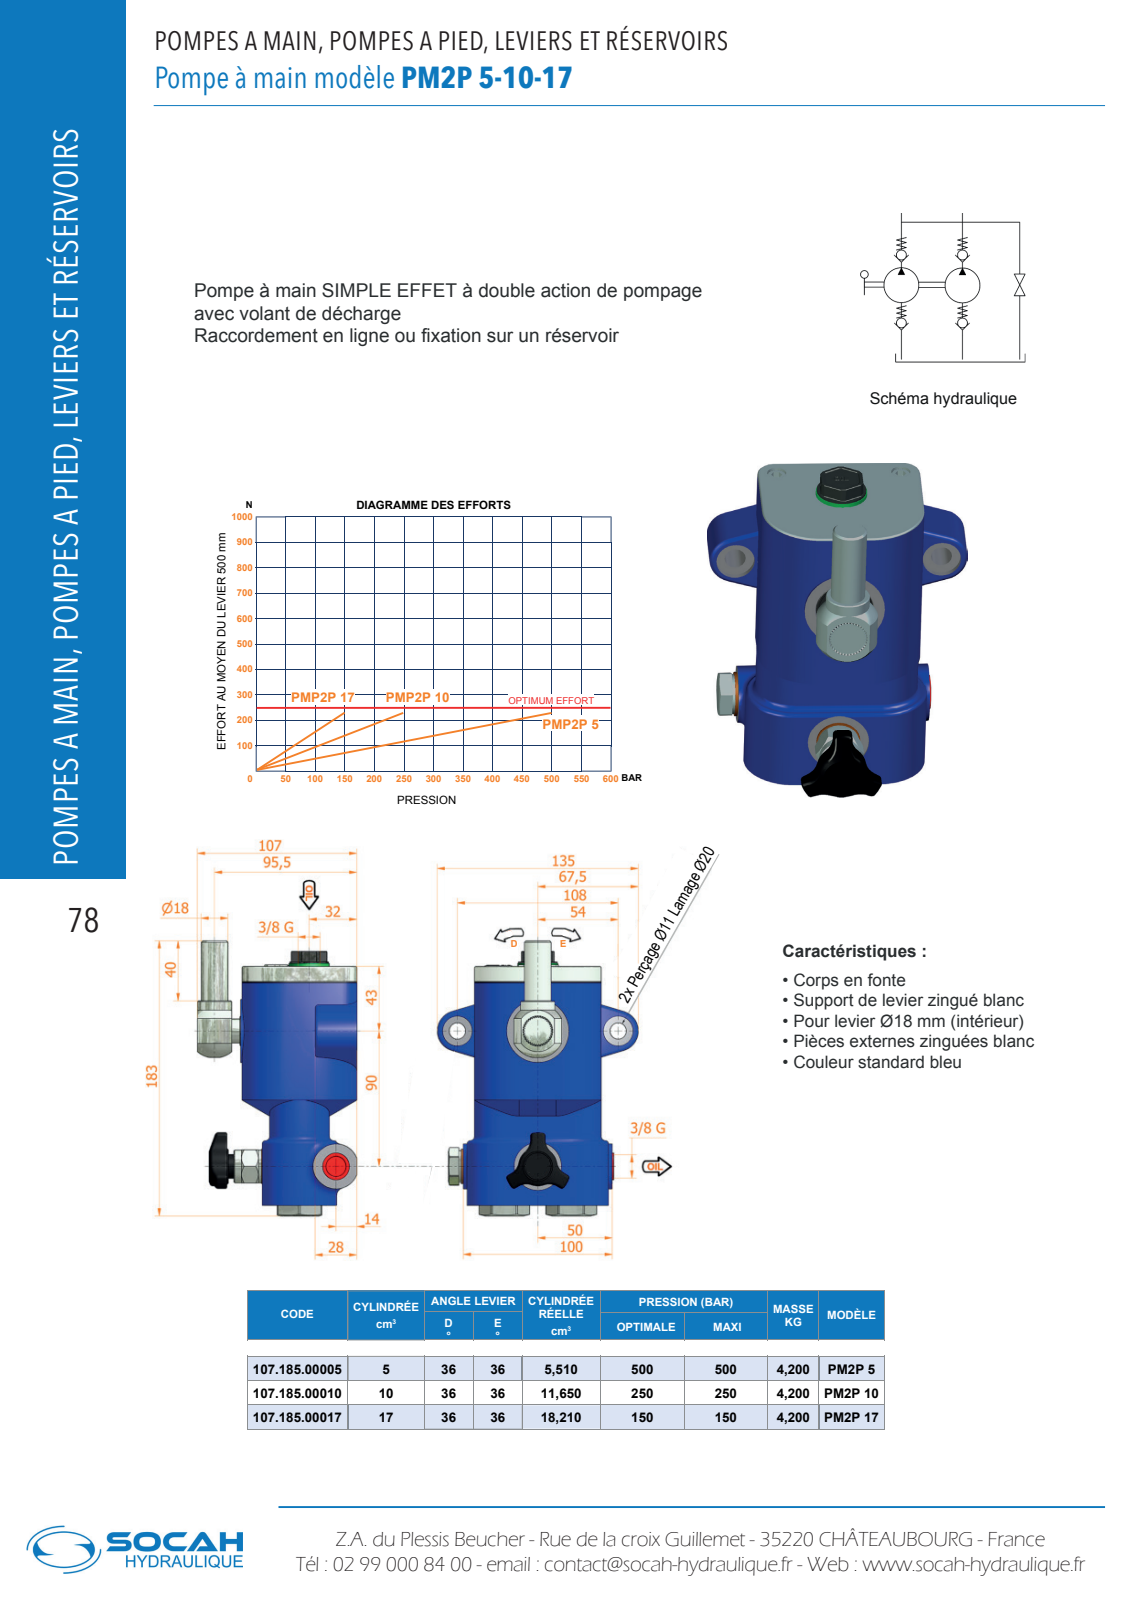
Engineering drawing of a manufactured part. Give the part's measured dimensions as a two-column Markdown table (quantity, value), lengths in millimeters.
| quantity | value |
| --- | --- |
| part name | 6092.0000.00.50 Bloccato |
| STEP written by | Autodesk Inventor 2010 (AUTOMOTIVE_DESIGN) |
| units | millimeters |
| bodies | 0 solids, 1942 faces (599 planar, 665 cylindrical, 678 other) |
| overall size | 183.1 × 135 × 107 |
| round holes (diameter × count) | 10 × 2, 18 × 2, 25 × 2, 28.5 × 2, 4.92 × 1, 17 × 1, 21 × 1, 27 × 1 |
| round bosses / shafts (diameter × count) | 23 × 3, 24 × 2, 16 × 2, 14 × 2, 6 × 2, 42 × 1, 27 × 1, 26 × 1 |
| partial cylindrical surfaces (radius × count) | 5.46 × 76, 5.48 × 76, 0.5 × 24, 2 × 23, 1 × 13, 0.15 × 12, 0.2 × 12, 10 × 8 |
| main face-to-face distances | 6, 5, 85, 79, 71, 159.1, 80, 154.1, 74.1, 73 |
| hole center spacings | 61.28, 45, 90.1 |
